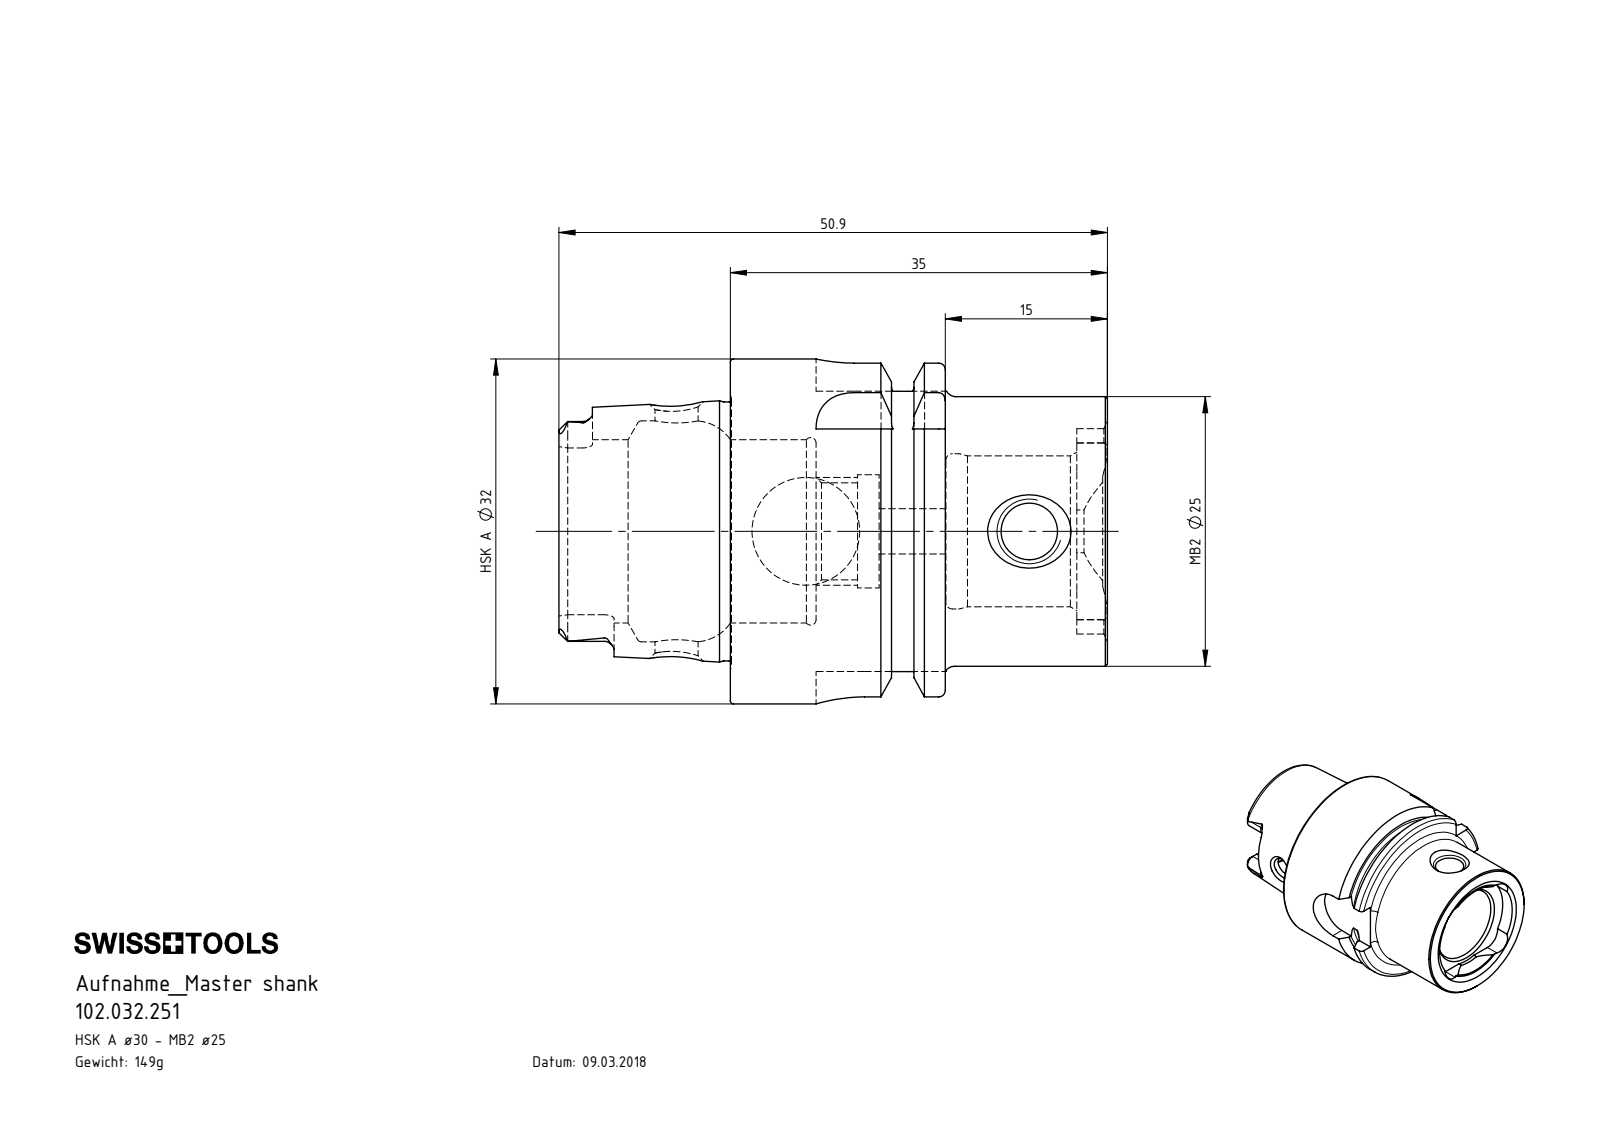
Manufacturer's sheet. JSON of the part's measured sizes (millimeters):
{"part_name": "102.032.251", "step_written_by": "SolidWorks 2017 (CONFIG_CONTROL_DESIGN)", "units": "millimeters", "bodies": {"solids": 1, "faces": 196, "planar": 57, "cylindrical": 64, "other": 75}, "overall_size": [50.9, 32, 32], "volume_mm3": 19007, "surface_area_mm2": 8601, "round_holes": [[4, 1], [4.2, 1], [5.25, 1], [9, 1], [10, 1], [10.5, 1], [14, 1], [14.4, 1], [17, 1], [20.5, 1]], "round_bosses_or_shafts": [[32, 1], [26.45, 1], [25, 1], [24.03, 1]], "partial_cylinders_radius": [[0.9, 8], [1.38, 4], [2.7, 4], [3.5, 2], [4.5, 1], [8, 1], [9.53, 1]], "face_to_face_distances": [35, 20, 19.95, 15.05, 15, 7.95, 12, 27.05, 12.05, 32.15], "hole_center_spacings": [20.75]}
